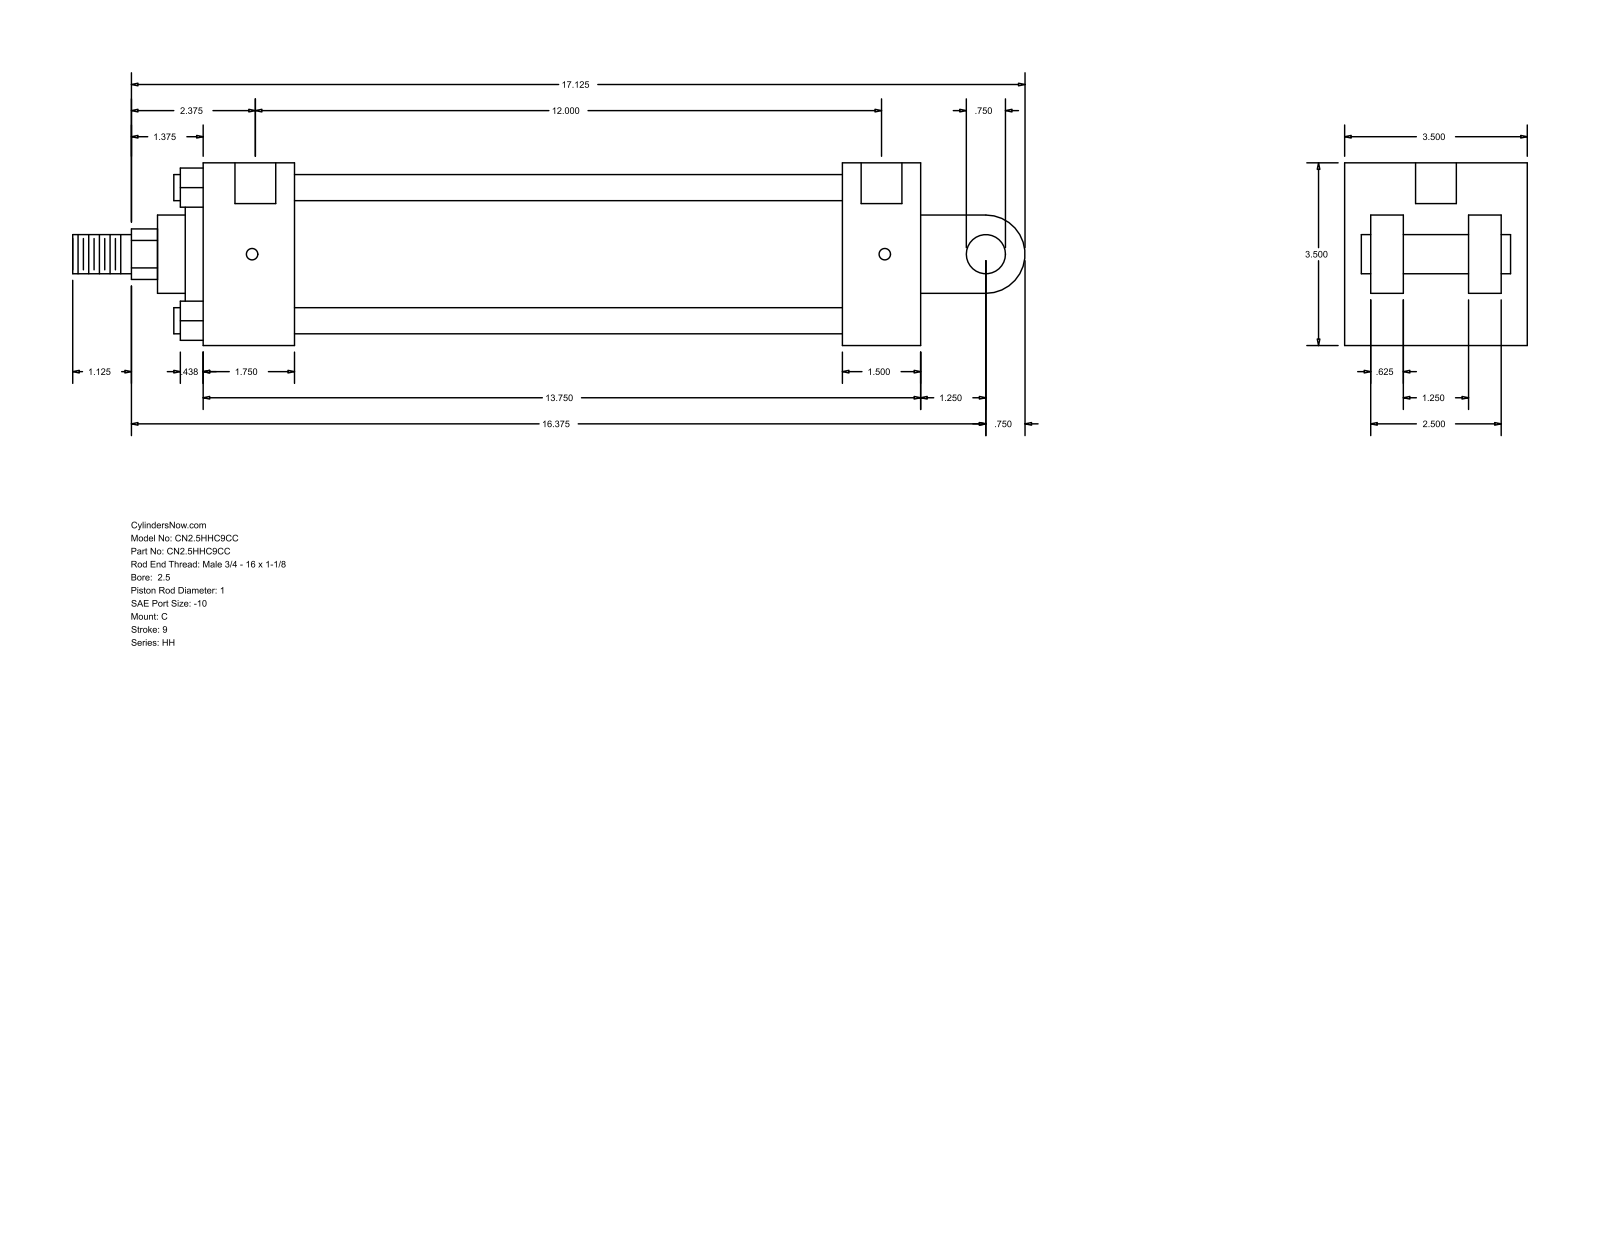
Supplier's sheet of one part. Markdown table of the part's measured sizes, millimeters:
| quantity | value |
| --- | --- |
| part name | HH_C__0250_1 |
| STEP written by | GSSL Pune (CONFIG_CONTROL_DESIGN) |
| units | millimeters |
| bodies | 0 solids, 101 faces (71 planar, 30 cylindrical, 0 other) |
| overall size | 463.55 × 88.9 × 88.9 |
| round holes (diameter × count) | 5.56 × 4, 19.84 × 2 |
| round bosses / shafts (diameter × count) | 12.7 × 4, 19.05 × 2, 73.03 × 1, 60.33 × 1, 38.1 × 1, 25.4 × 1 |
| partial cylindrical surfaces (radius × count) | 12.29 × 1, 19.05 × 1 |
| main face-to-face distances | 88.9, 349.26, 63.5, 311.15, 38.11, 44.46, 266.69, 304.8, 12.7, 28.57 |
| hole center spacings | 1.59, 306.38, 307.97, 304.79 |
